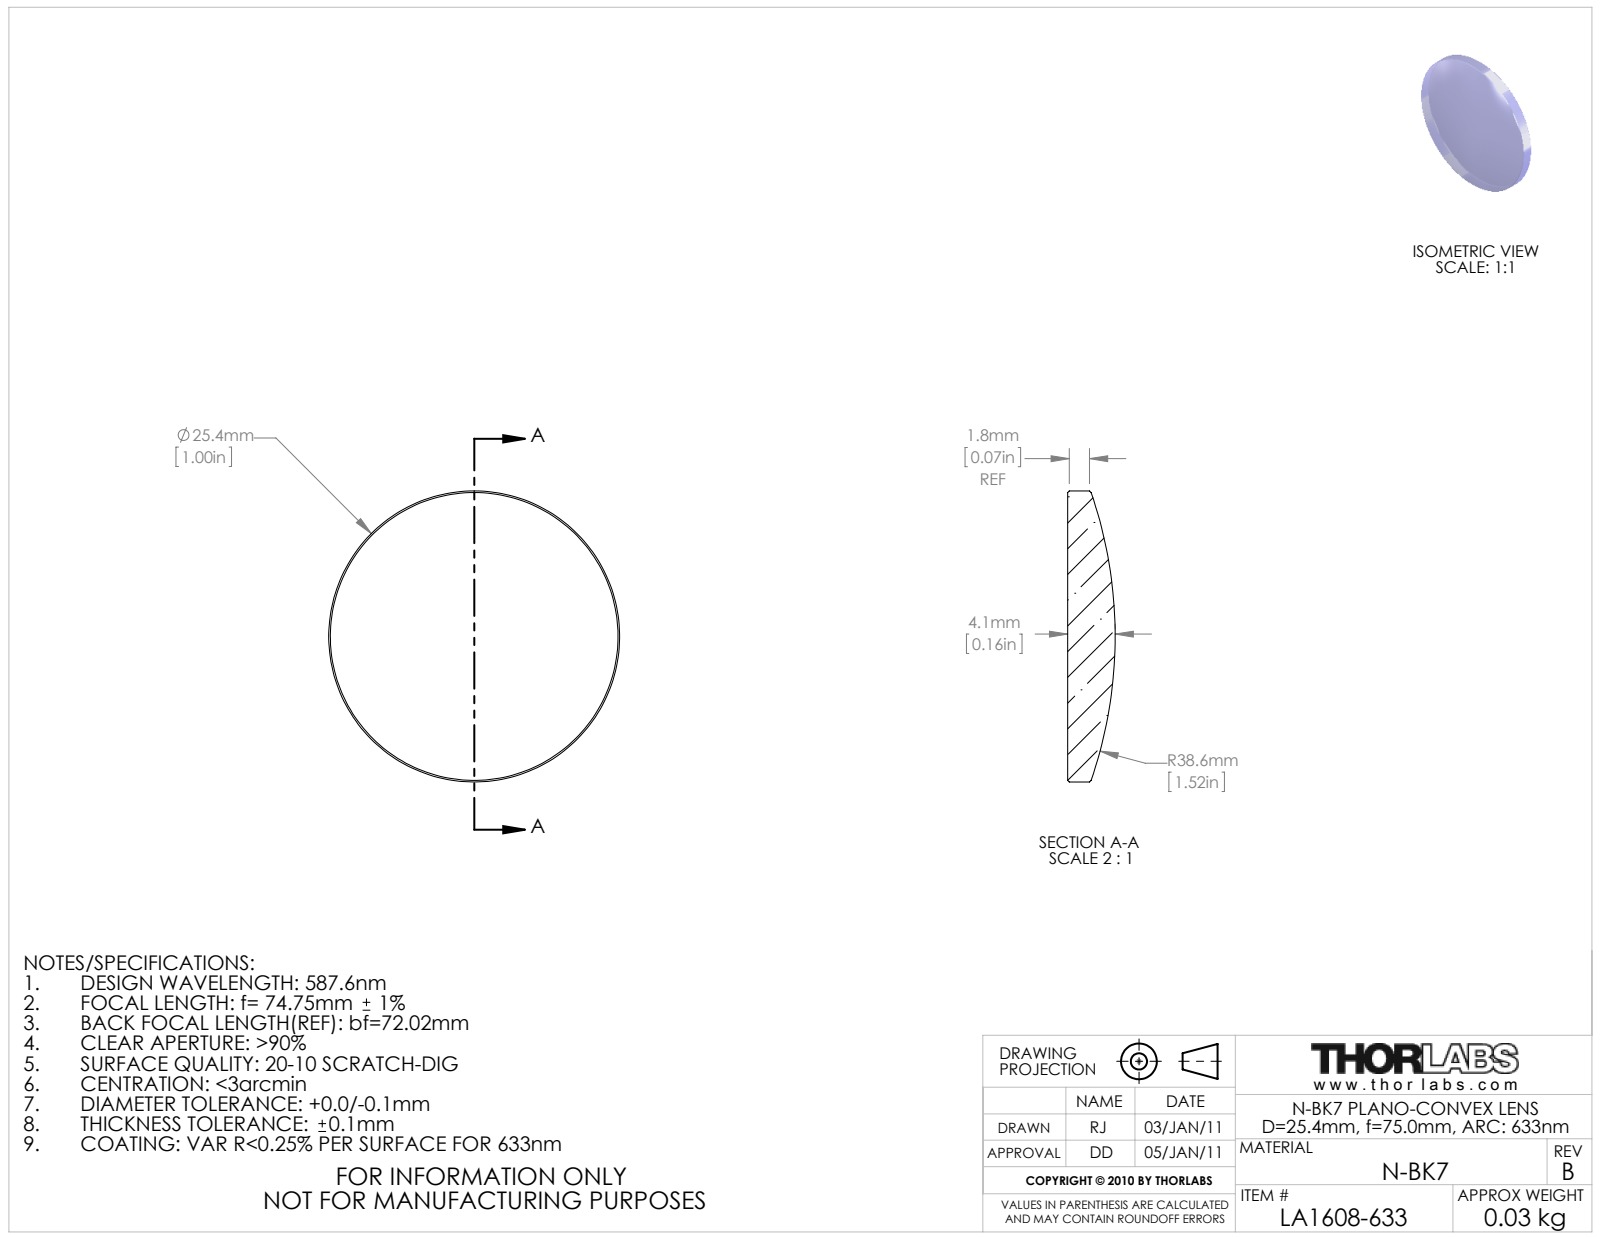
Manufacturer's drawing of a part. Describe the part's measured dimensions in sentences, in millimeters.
The part is named "21789-E0W". Its 3-D file was written by "SolidWorks 2011 (AUTOMOTIVE_DESIGN)". It is 0 solids with 9 faces: 1 planar, 2 cylindrical and 6 other. Overall it measures 25.4 by 25.4 by 4.14 millimeters. Round bosses or shafts: 1 of diameter 25.4.
